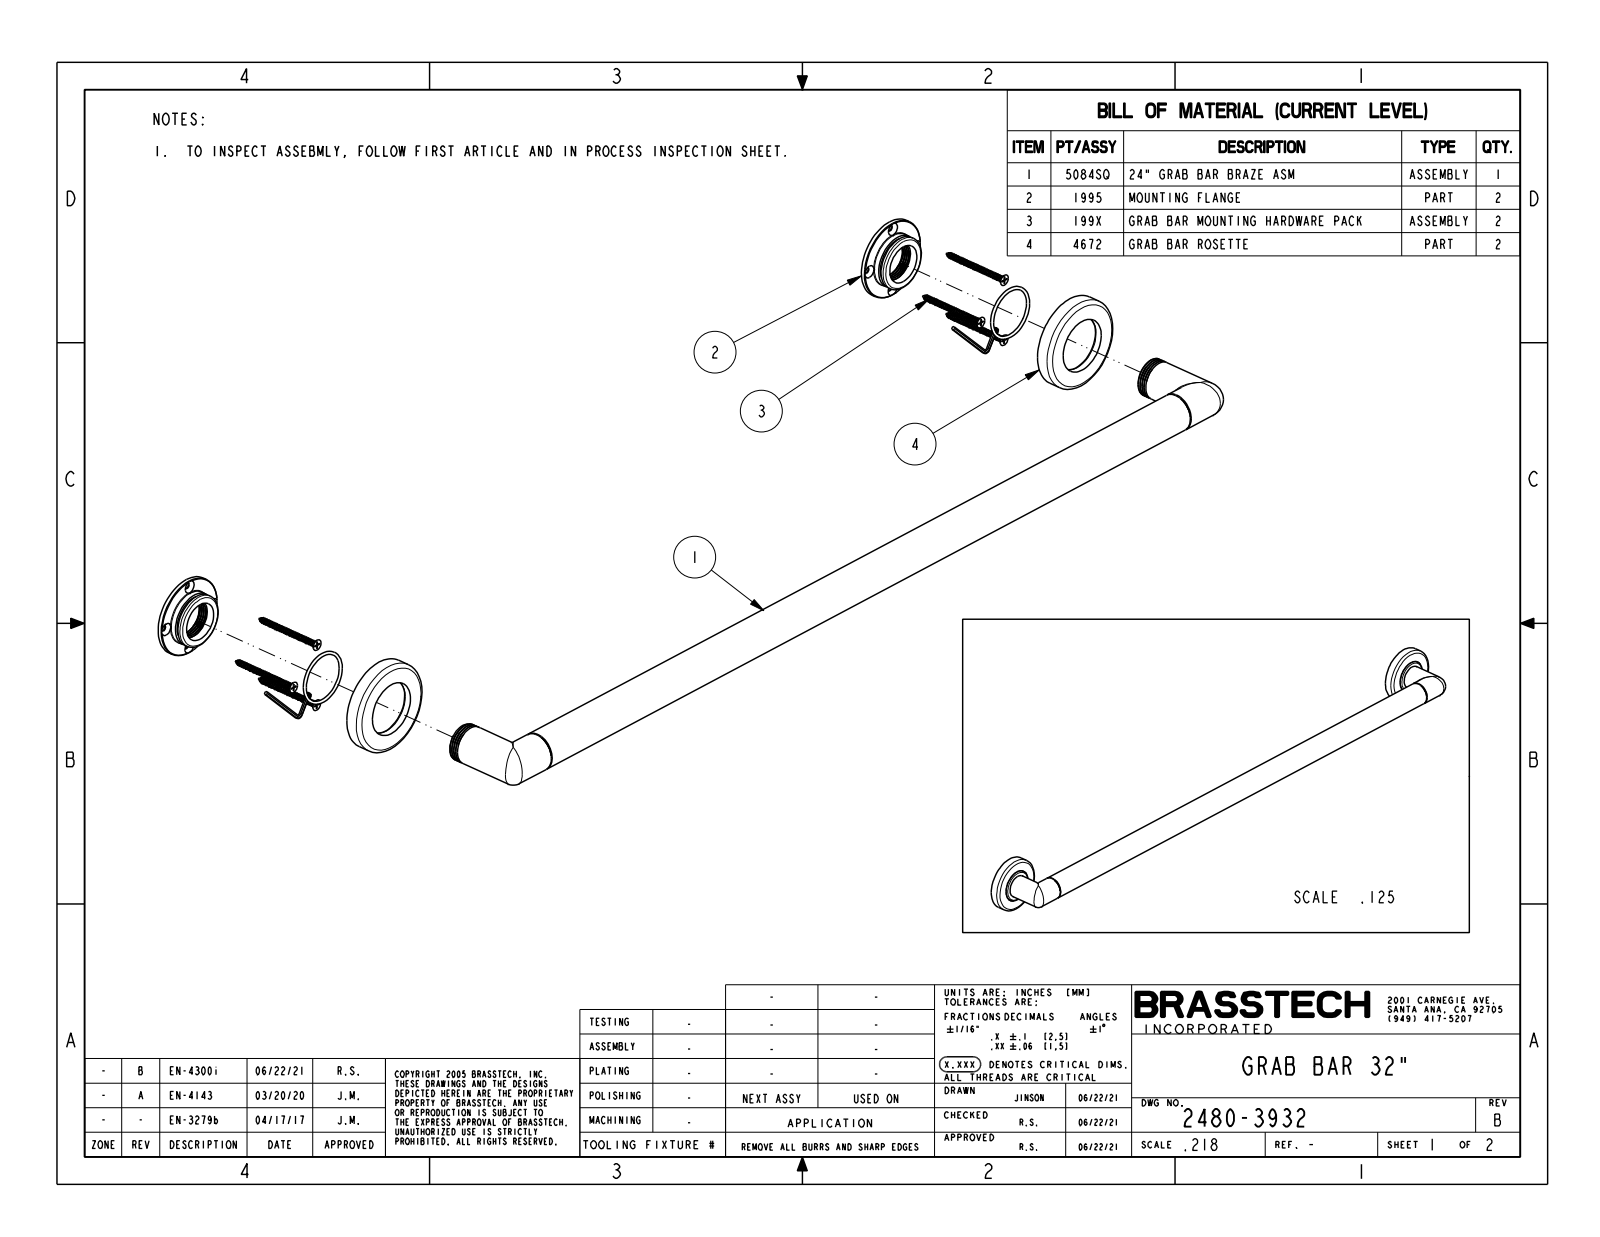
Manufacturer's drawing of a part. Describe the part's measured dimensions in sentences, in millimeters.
The part is named "2480-3932". Its 3-D file was written by "CREO PARAMETRIC BY PTC INC, 2018400 (CONFIG_CONTROL_DESIGN)". It is 1 solid with 48 faces: 6 planar, 18 cylindrical and 24 other. Overall it measures 889 by 76.2 by 70 millimeters. Its volume is 831 300 cubic millimeters and its surface area 111 400 square millimeters. Round bosses or shafts: 3 of diameter 31.8, 2 of diameter 76.2, 2 of diameter 44.5. The main face-to-face distances are 13.5, 15.2, 1.8.
